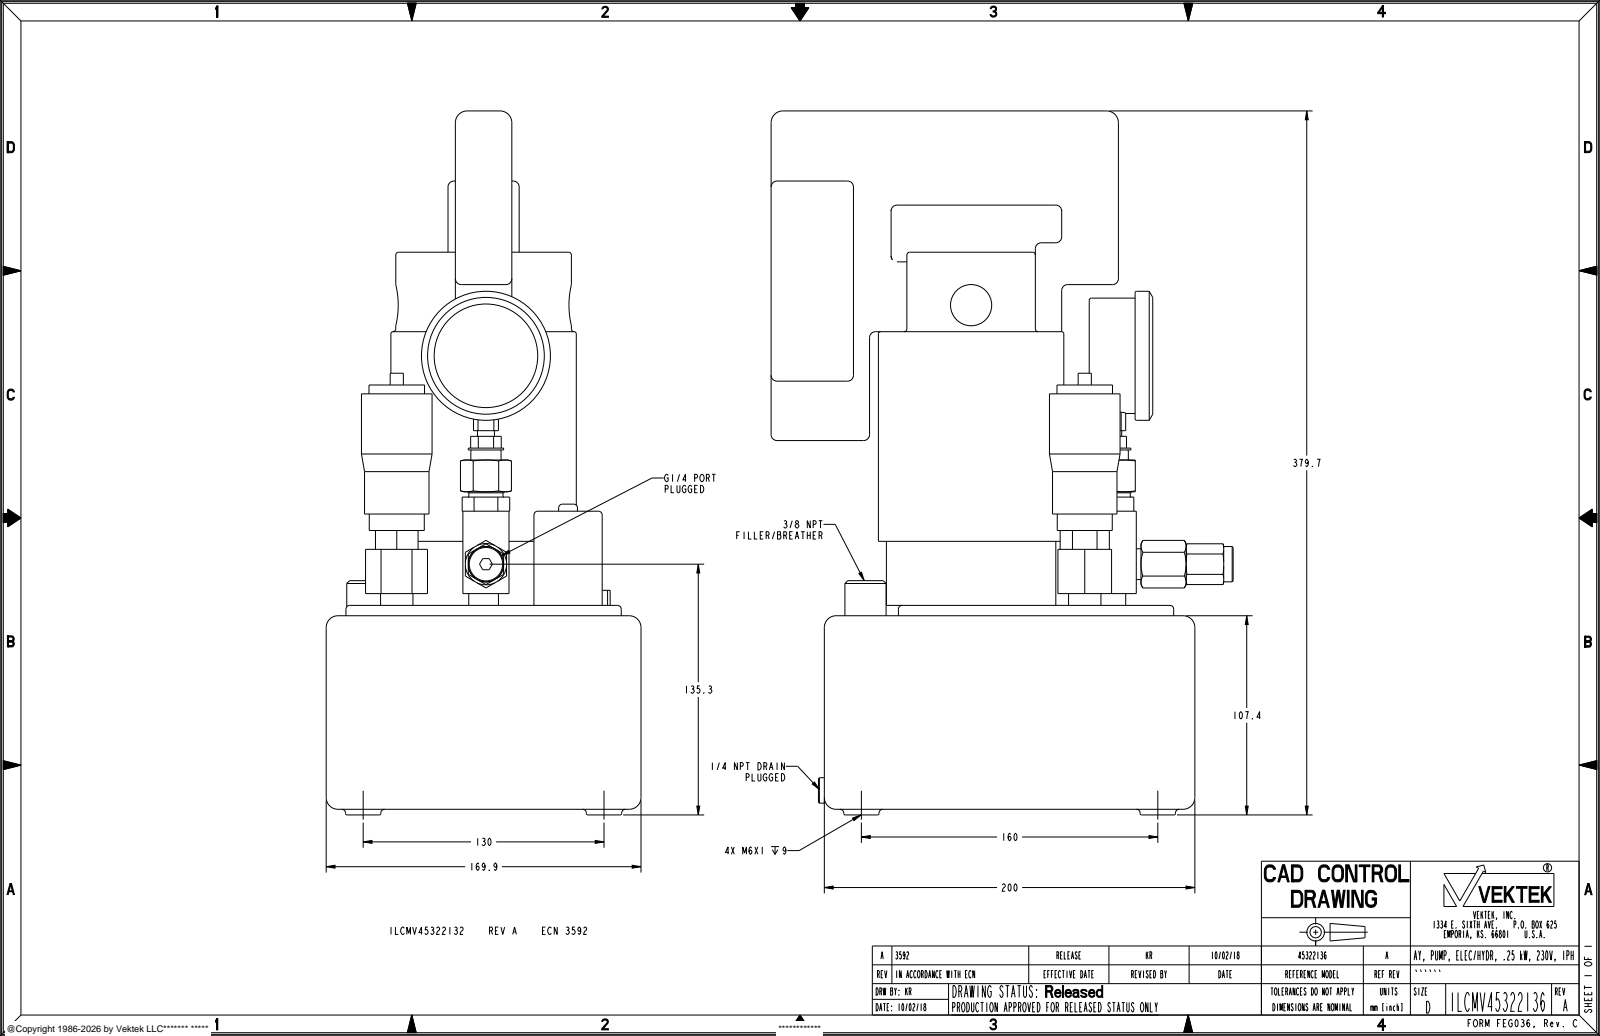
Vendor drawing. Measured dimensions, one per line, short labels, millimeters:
name: ILCMV45322136
written by: PRO/ENGINEER BY PARAMETRIC TECHNOLOGY CORPORATION, 2013320 (AUTOMOTIVE_DESIGN)
unit: mm
bodies: 1 solid, 501 faces (164 planar, 168 cylindrical, 169 other)
size: 379.73 × 249.38 × 169.93
volume: 5 954 000 mm³; area: 314 615 mm²
holes: 4× ⌀5, 1× ⌀11.89, 1× ⌀16.56, 1× ⌀22.23, 1× ⌀24.13, 1× ⌀55.88
bosses: 6× ⌀19.05, 1× ⌀148.59, 1× ⌀100.08, 1× ⌀91.44, 1× ⌀69.6, 1× ⌀62.23, 1× ⌀38.1, 1× ⌀36.83
rounds: 44× R3.17, 22× R6.35, 8× R1.52, 1× R7.98, 1× R47.4
face distances: 69.72, 100.2, 169.92, 200, 104.39, 30.48, 109.98, 5.59, 3.96, 65.76
hole spacings: 130, 160, 206.16, 3.17, 68.12, 70.51, 112.39, 127.76
